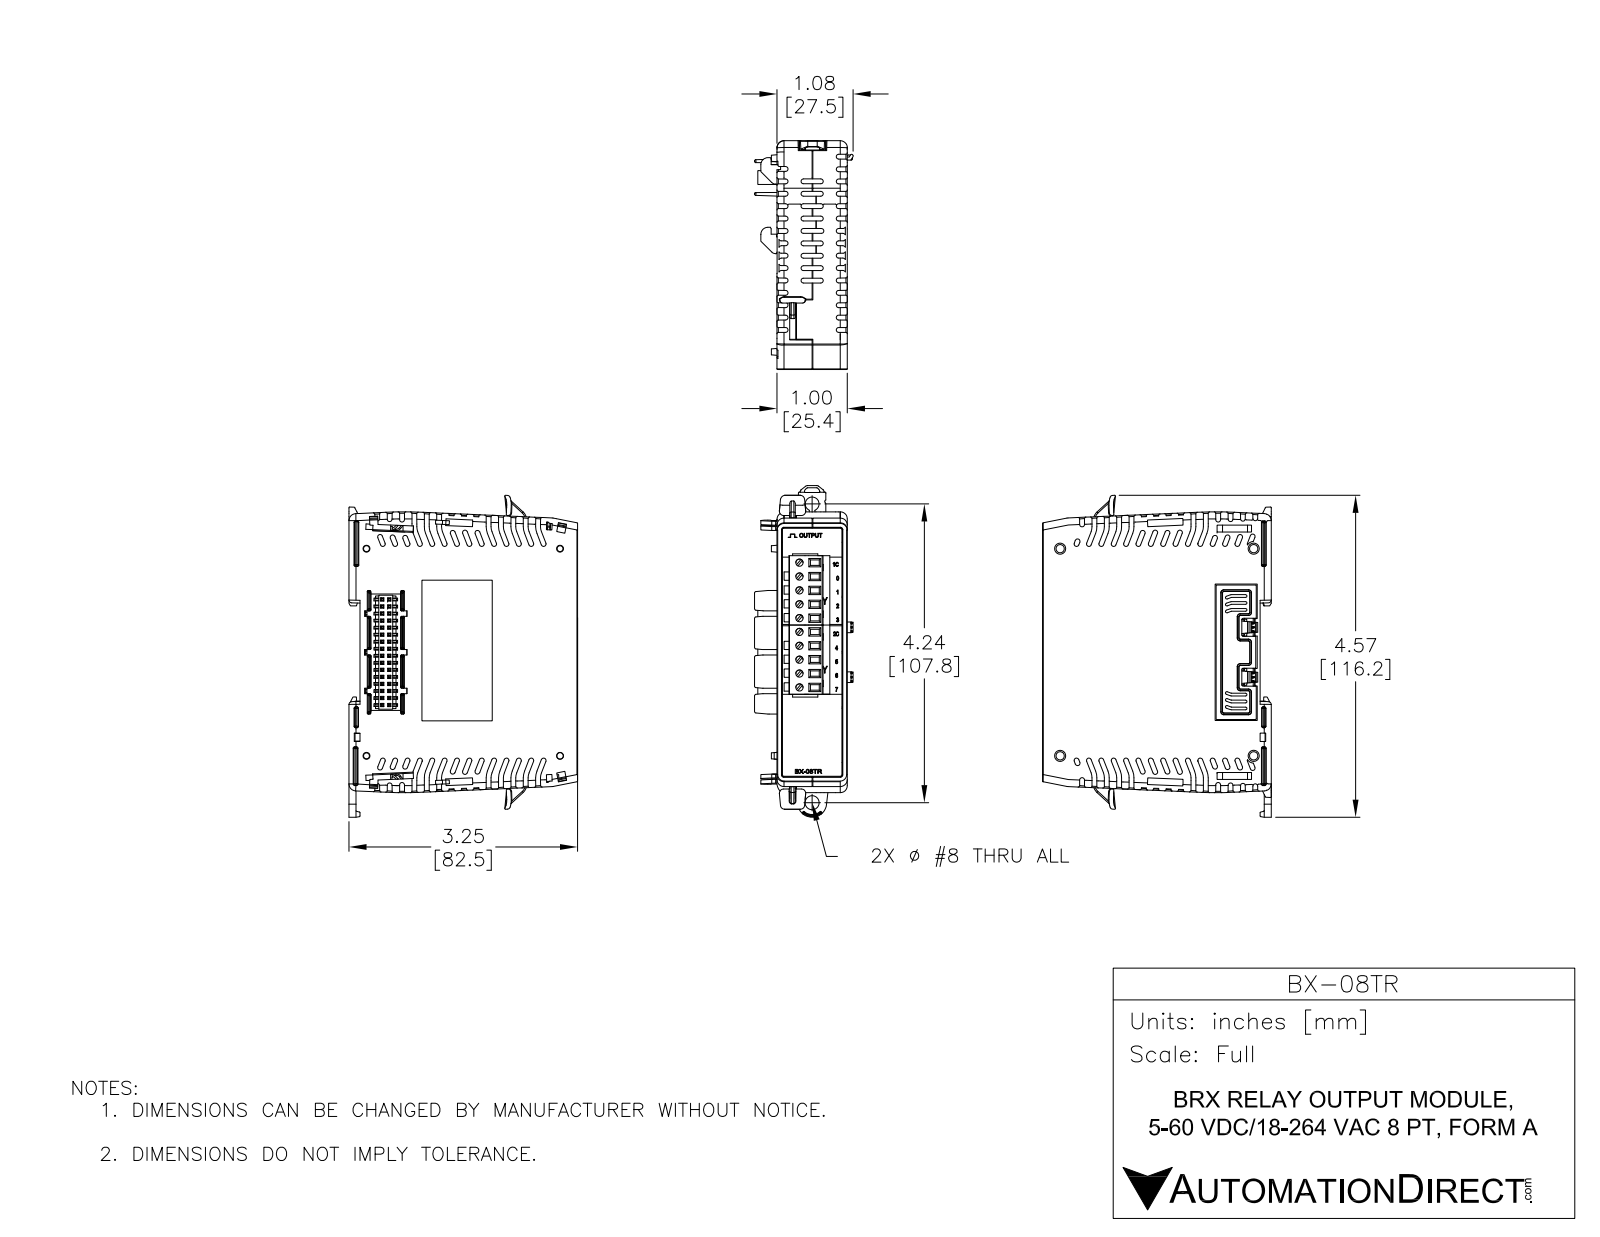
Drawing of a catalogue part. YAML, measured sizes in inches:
part_name: "BX-08TR"
step_written_by: "SolidWorks 2017 (AUTOMOTIVE_DESIGN)"
units: inches
bodies: {solids: 22, faces: 3579, planar: 2540, cylindrical: 563, other: 476}
overall_size: [4.586, 3.311, 1.402]
volume: 11.59
surface_area: 72.76
round_holes:
  - {diameter: 0.047, count: 2}
  - {diameter: 0.065, count: 2}
  - {diameter: 0.118, count: 2}
  - {diameter: 0.118, count: 2}
  - {diameter: 0.199, count: 1}
round_bosses_or_shafts:
  - {diameter: 0.062, count: 2}
  - {diameter: 0.059, count: 2}
partial_cylinders:
  - {radius: 0.005, count: 102}
  - {radius: 0.01, count: 47}
  - {radius: 0.02, count: 34}
  - {radius: 0.005, count: 24}
  - {radius: 0.008, count: 21}
  - {radius: 0.117, count: 14}
  - {radius: 0.039, count: 13}
  - {radius: 0.01, count: 12}
face_to_face_distances: [1, 3.211, 3.22, 0.475, 0.1, 0.157, 3.053, 3.063, 0.787, 0.63]
hole_center_spacings: [0.1, 0.824, 0.919, 1.3, 2.093, 2.193, 2.585, 2.617]
